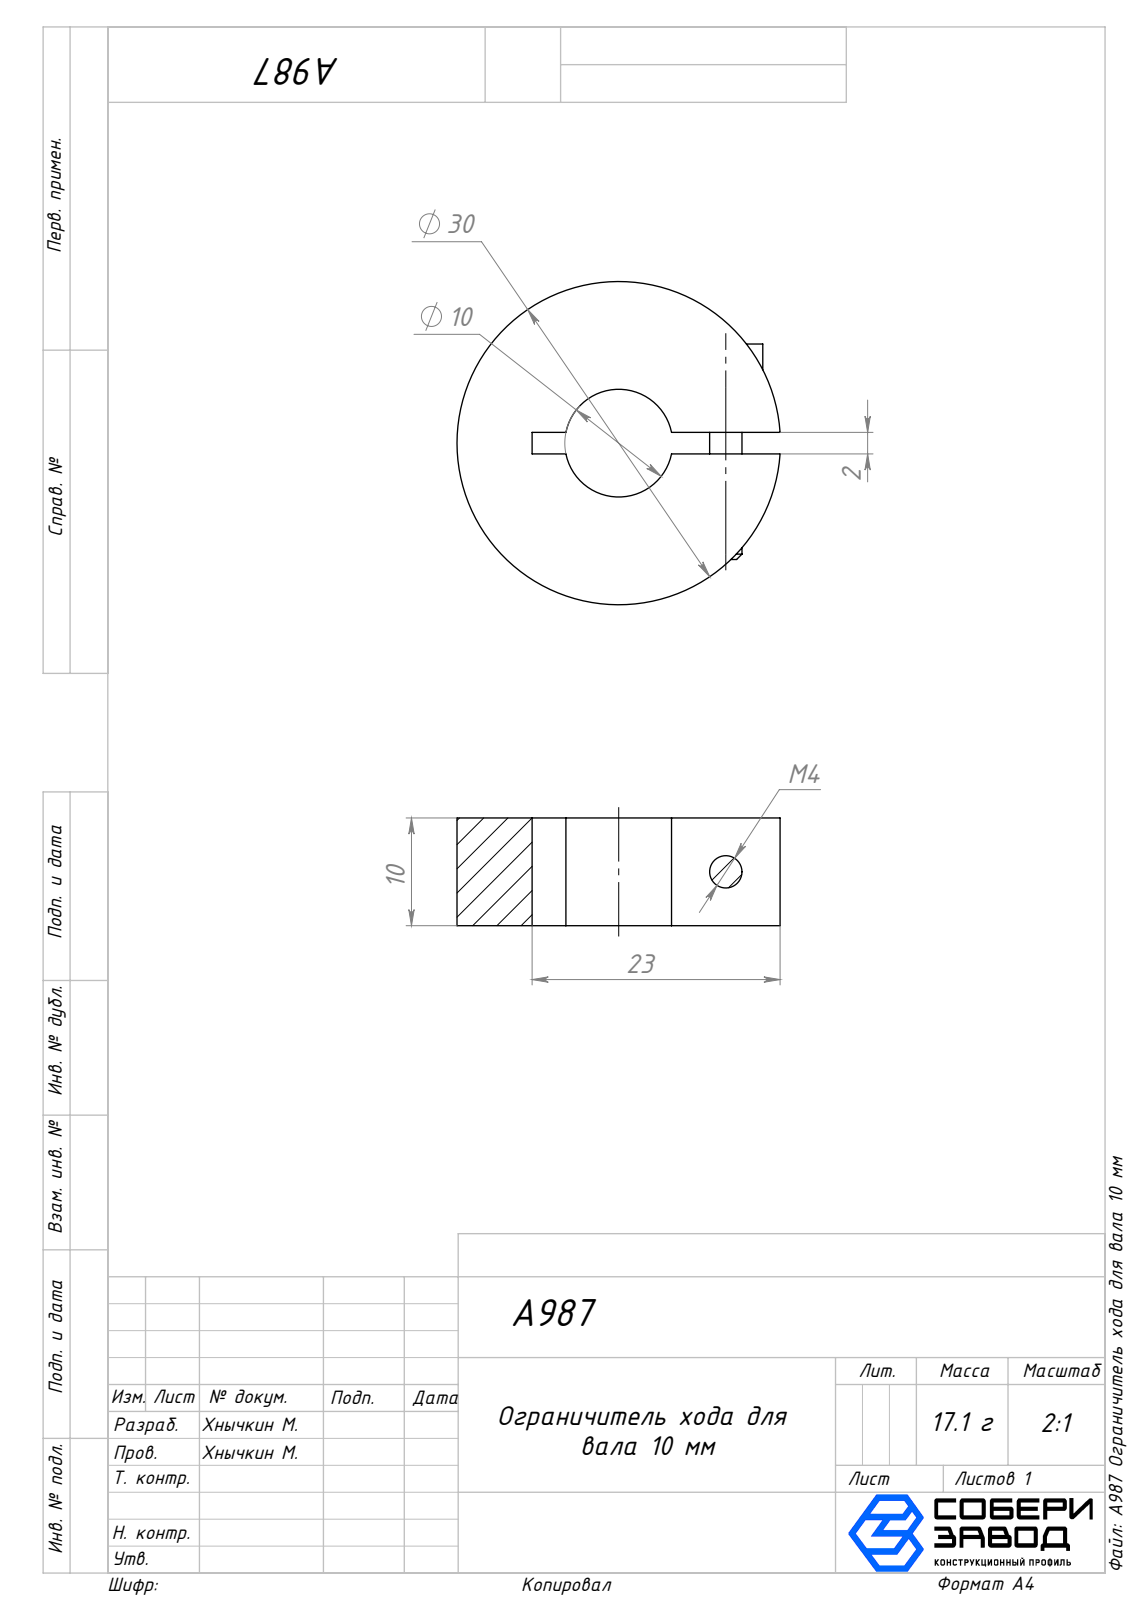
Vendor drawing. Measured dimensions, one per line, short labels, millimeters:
name: A987 Ограничитель хода для вала 10 мм; A987 Ограничитель_00; A987 Винт_00
written by: SolidWorks 2025 (AUTOMOTIVE_DESIGN)
unit: mm
bodies: 2 solids, 36 faces (18 planar, 16 cylindrical, 2 other)
size: 30 × 29.97 × 10
volume: 5 907 mm³; area: 3 235 mm²
holes: 1× ⌀3, 1× ⌀7.4, 1× ⌀10
bosses: 1× ⌀30, 1× ⌀6.86
face distances: 10, 2, 6.2, 4.2, 10.2, 8.2, 4, 3.4, 7.7, 5.7
